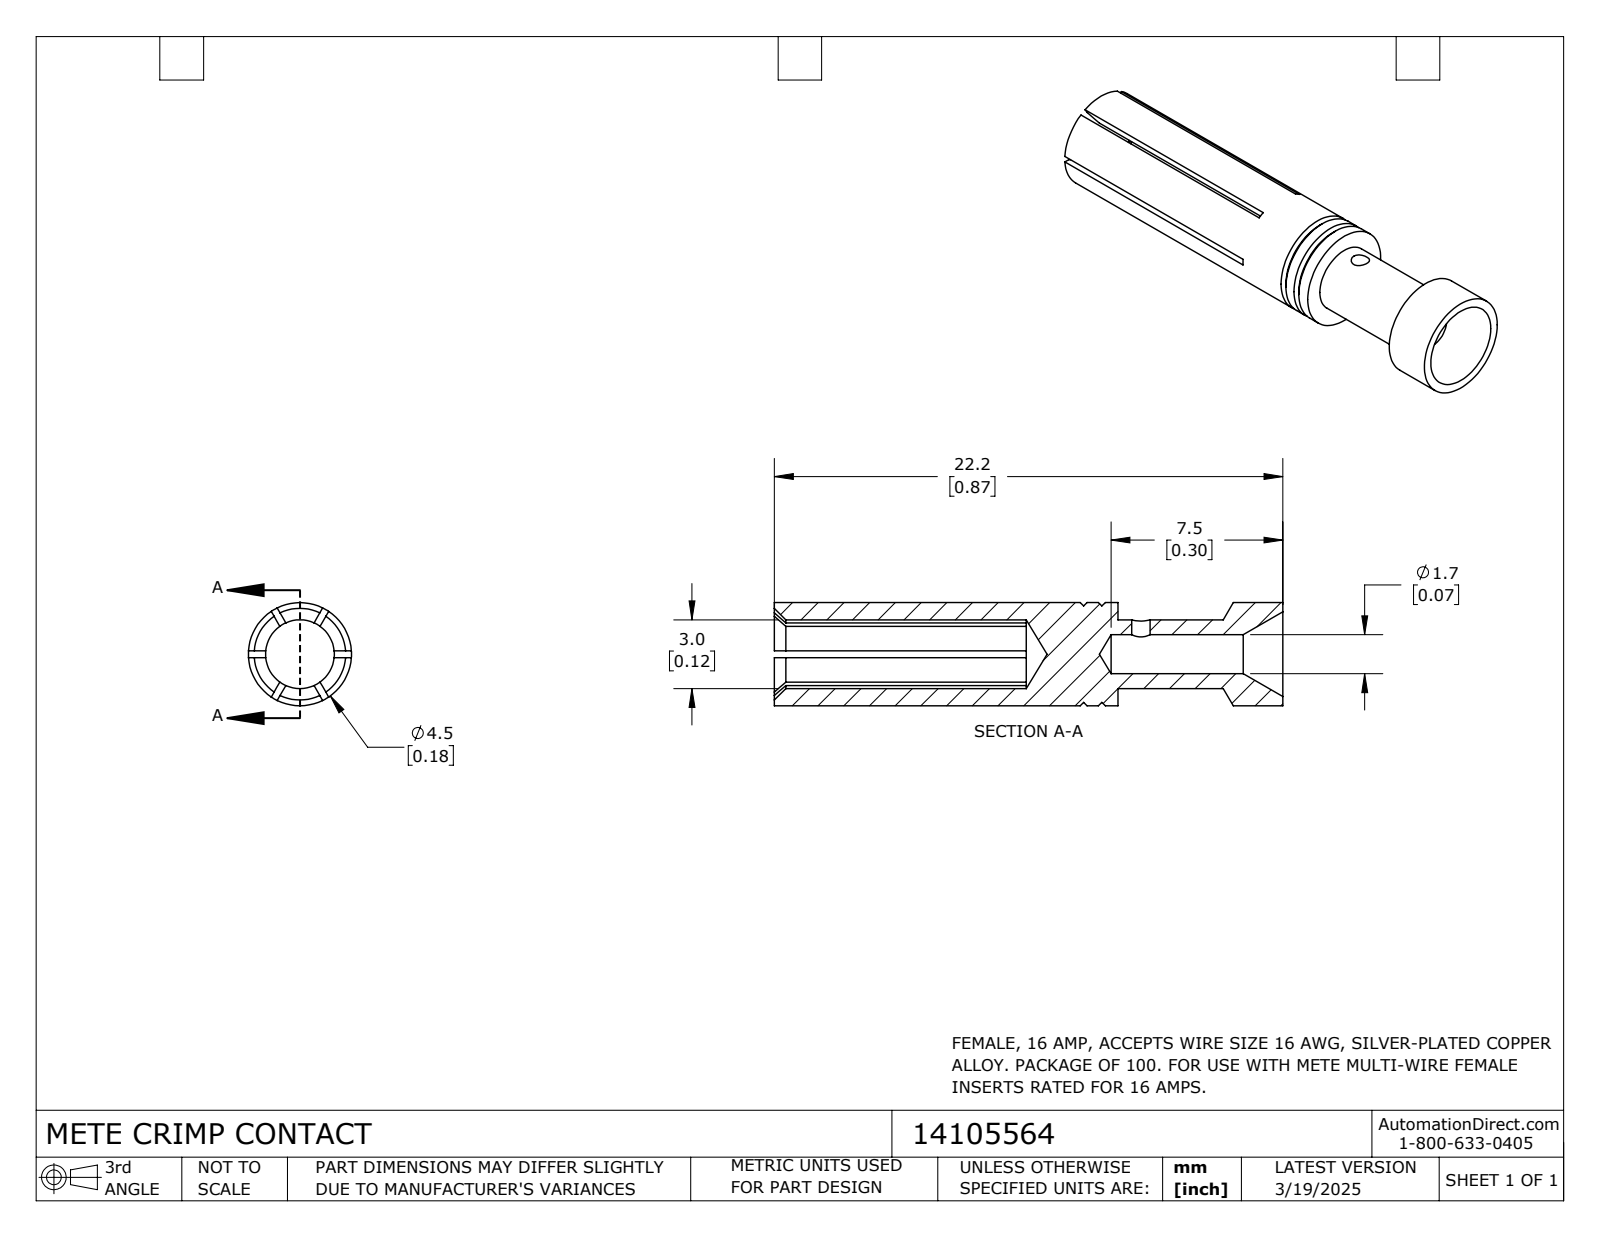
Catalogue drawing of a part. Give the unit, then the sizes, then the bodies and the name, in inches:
Units: inches
Overall size (bounding box): 0.874 × 0.177 × 0.177
Round holes (diameter × count): ⌀0.031 ×1, ⌀0.067 ×1, ⌀0.118 ×1
Round bosses / shafts (diameter × count): ⌀0.177 ×1
Main face-to-face distances: 0.283, 0.874, 0.591, 0.441, 0.157, 0.433
Volume: 0.012 in³ · Surface area: 0.839 in²
Bodies: 1 solid, 68 faces (26 planar, 20 cylindrical, 22 other)
Part name (STEP PRODUCT): 14105564
STEP written by: SolidWorks 2024 (CONFIG_CONTROL_DESIGN)
